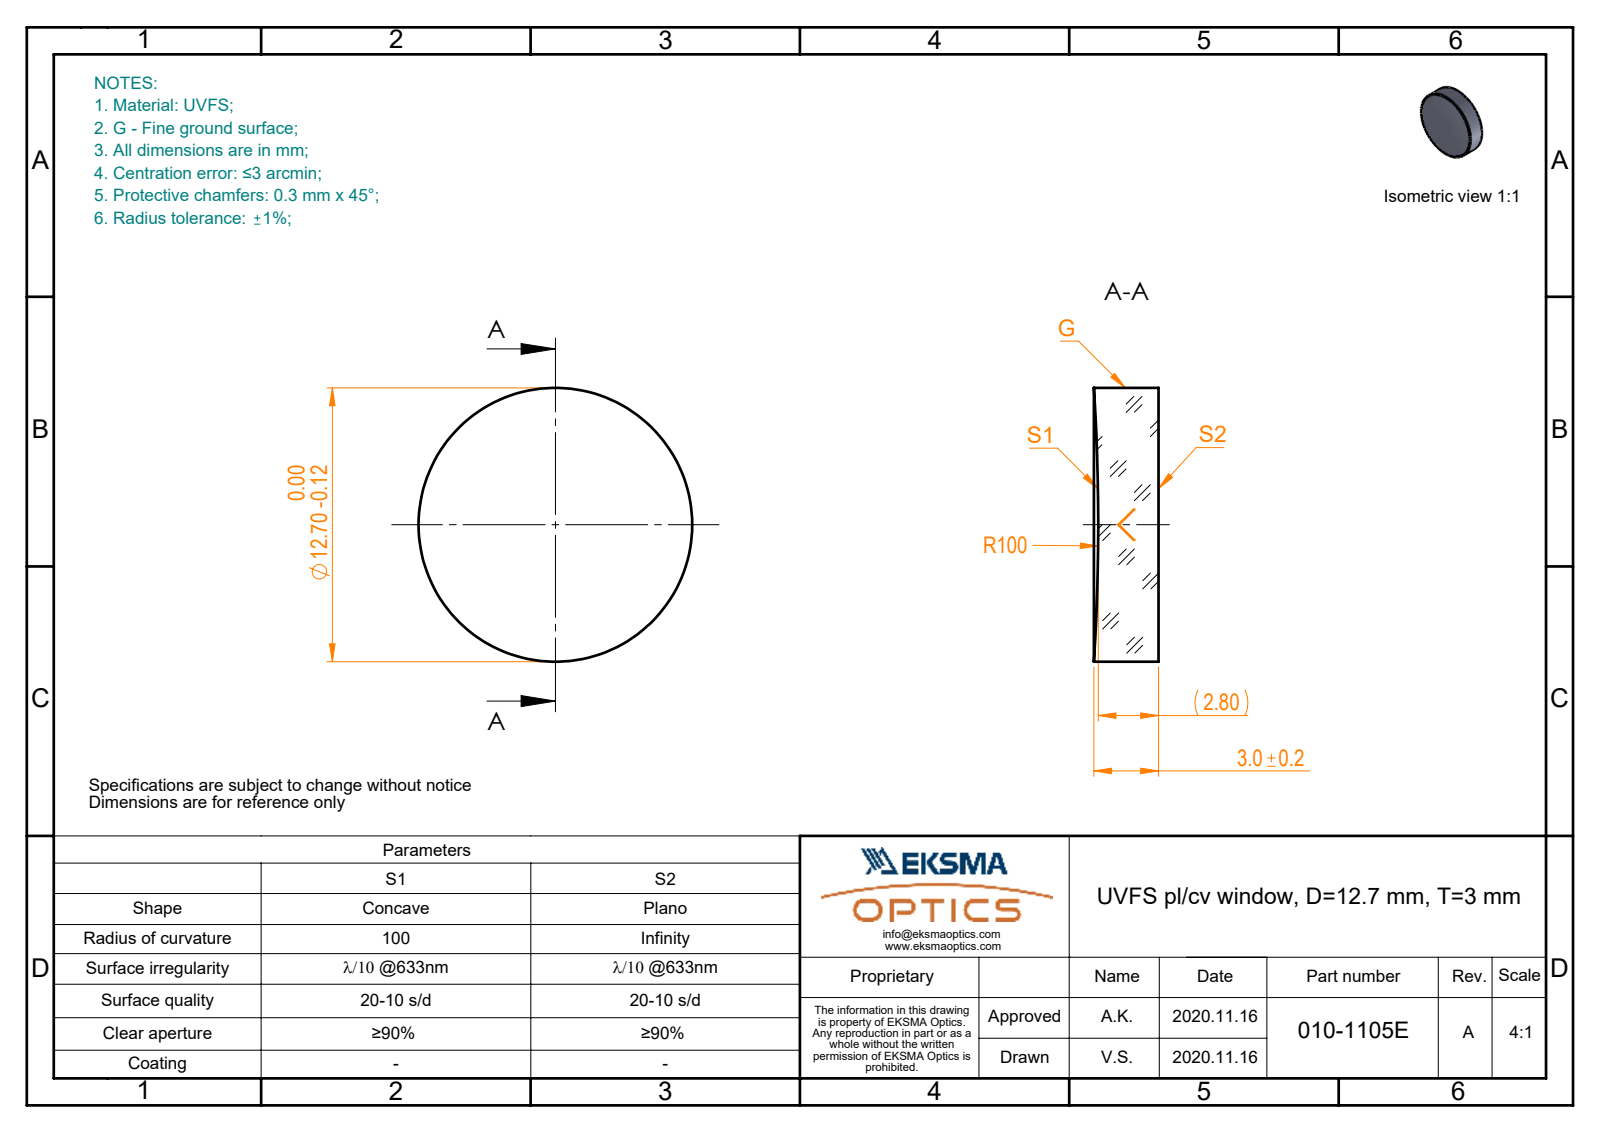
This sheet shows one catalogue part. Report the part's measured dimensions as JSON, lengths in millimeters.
{"part_name": "010-1105E_UVFS_PCV_window", "step_written_by": "SolidWorks 2019 (CONFIG_CONTROL_DESIGN)", "units": "millimeters", "bodies": {"solids": 1, "faces": 5, "planar": 1, "cylindrical": 2, "other": 2}, "overall_size": [12.7, 12.7, 3], "volume_mm3": 367, "surface_area_mm2": 373, "round_bosses_or_shafts": [[12.7, 1]]}
